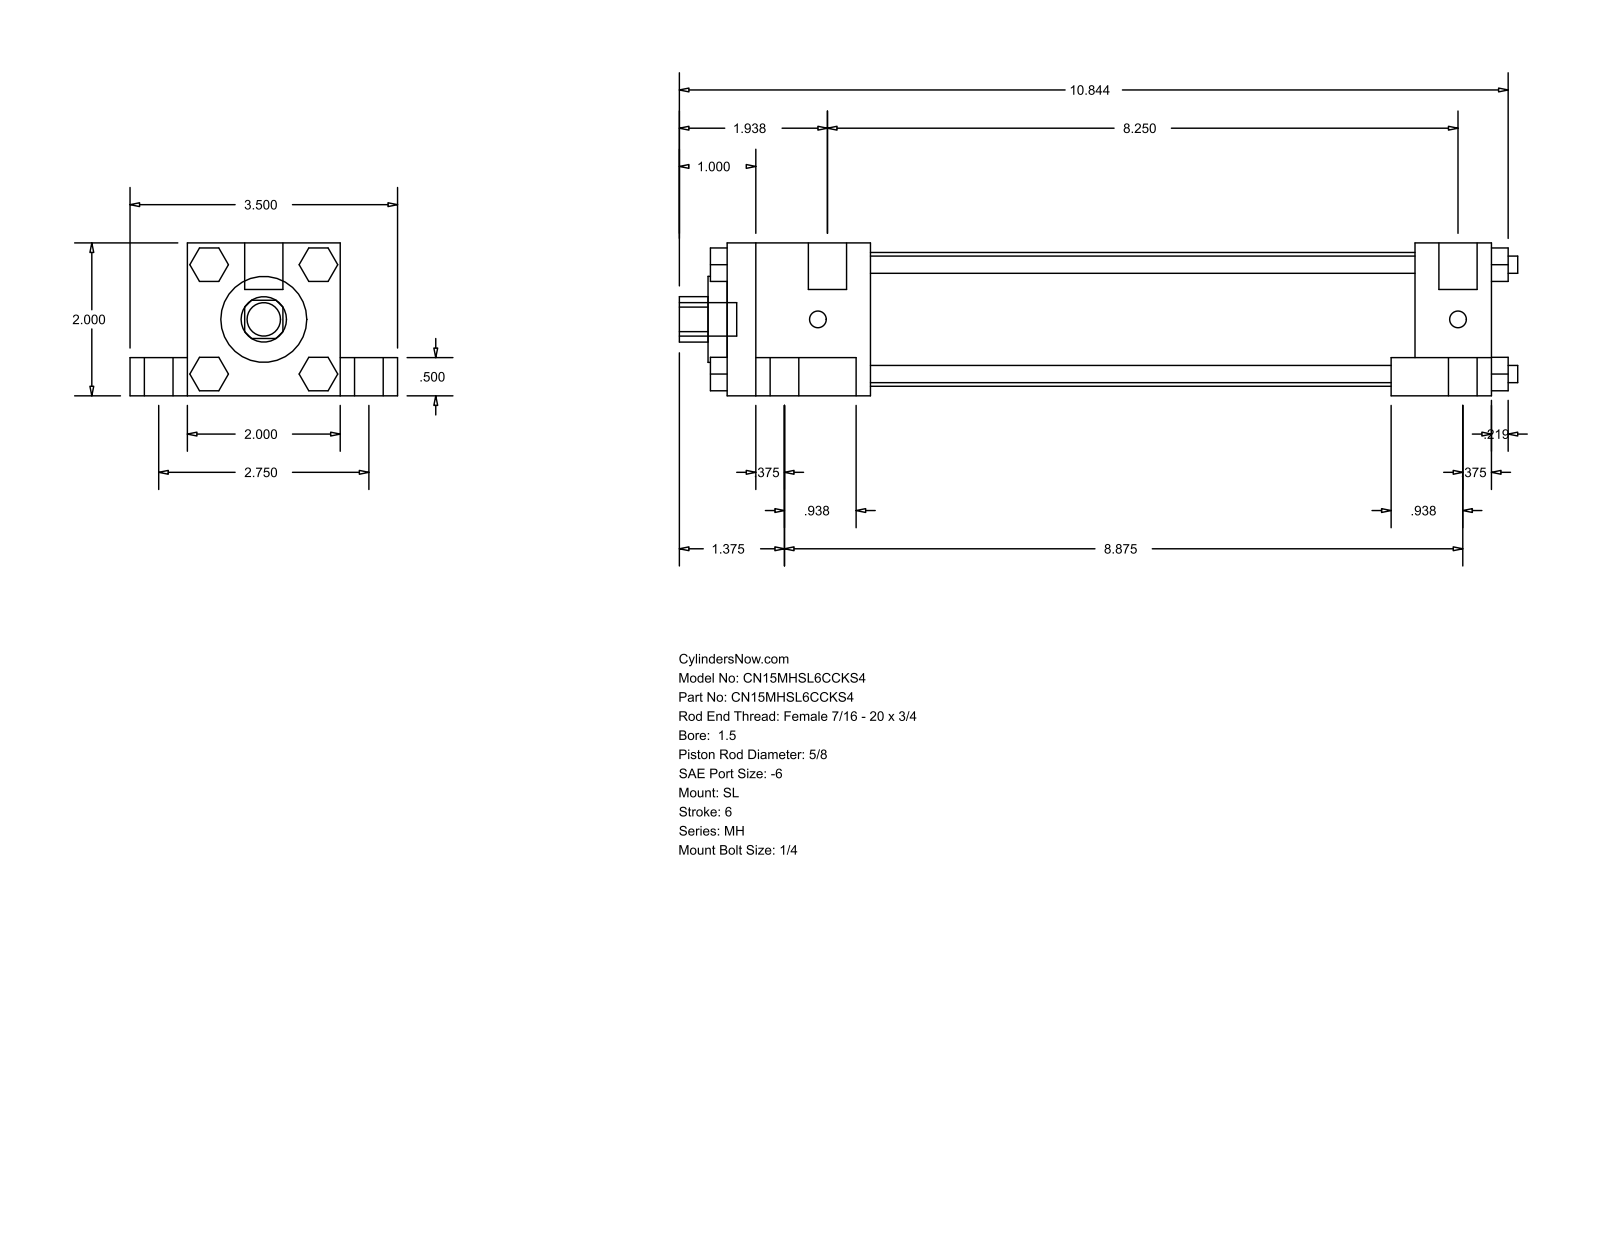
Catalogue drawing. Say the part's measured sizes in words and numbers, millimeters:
The part is named "MH_SL__0150_0.625". Its 3-D file was written by "GSSL Pune (CONFIG_CONTROL_DESIGN)". It is 0 solids with 148 faces: 112 planar, 36 cylindrical and 0 other. Overall it measures 278.61 by 88.9 by 50.8 millimeters. Round holes: 1 of diameter 15.88, 1 of diameter 28.57, 1 of diameter 44.45. Round bosses or shafts: 4 of diameter 15.88, 4 of diameter 9.53, 4 of diameter 5.71, 4 of diameter 5.56, 2 of diameter 12.7, 1 of diameter 11.11. Partial cylindrical surfaces (rounded edges, fillets, slot ends): 1 of radius 7.54. The main face-to-face distances are 50.8, 38.1, 19.05, 12.7, 69.85, 254, 9.52, 33.34, 211.14, 228.59.
